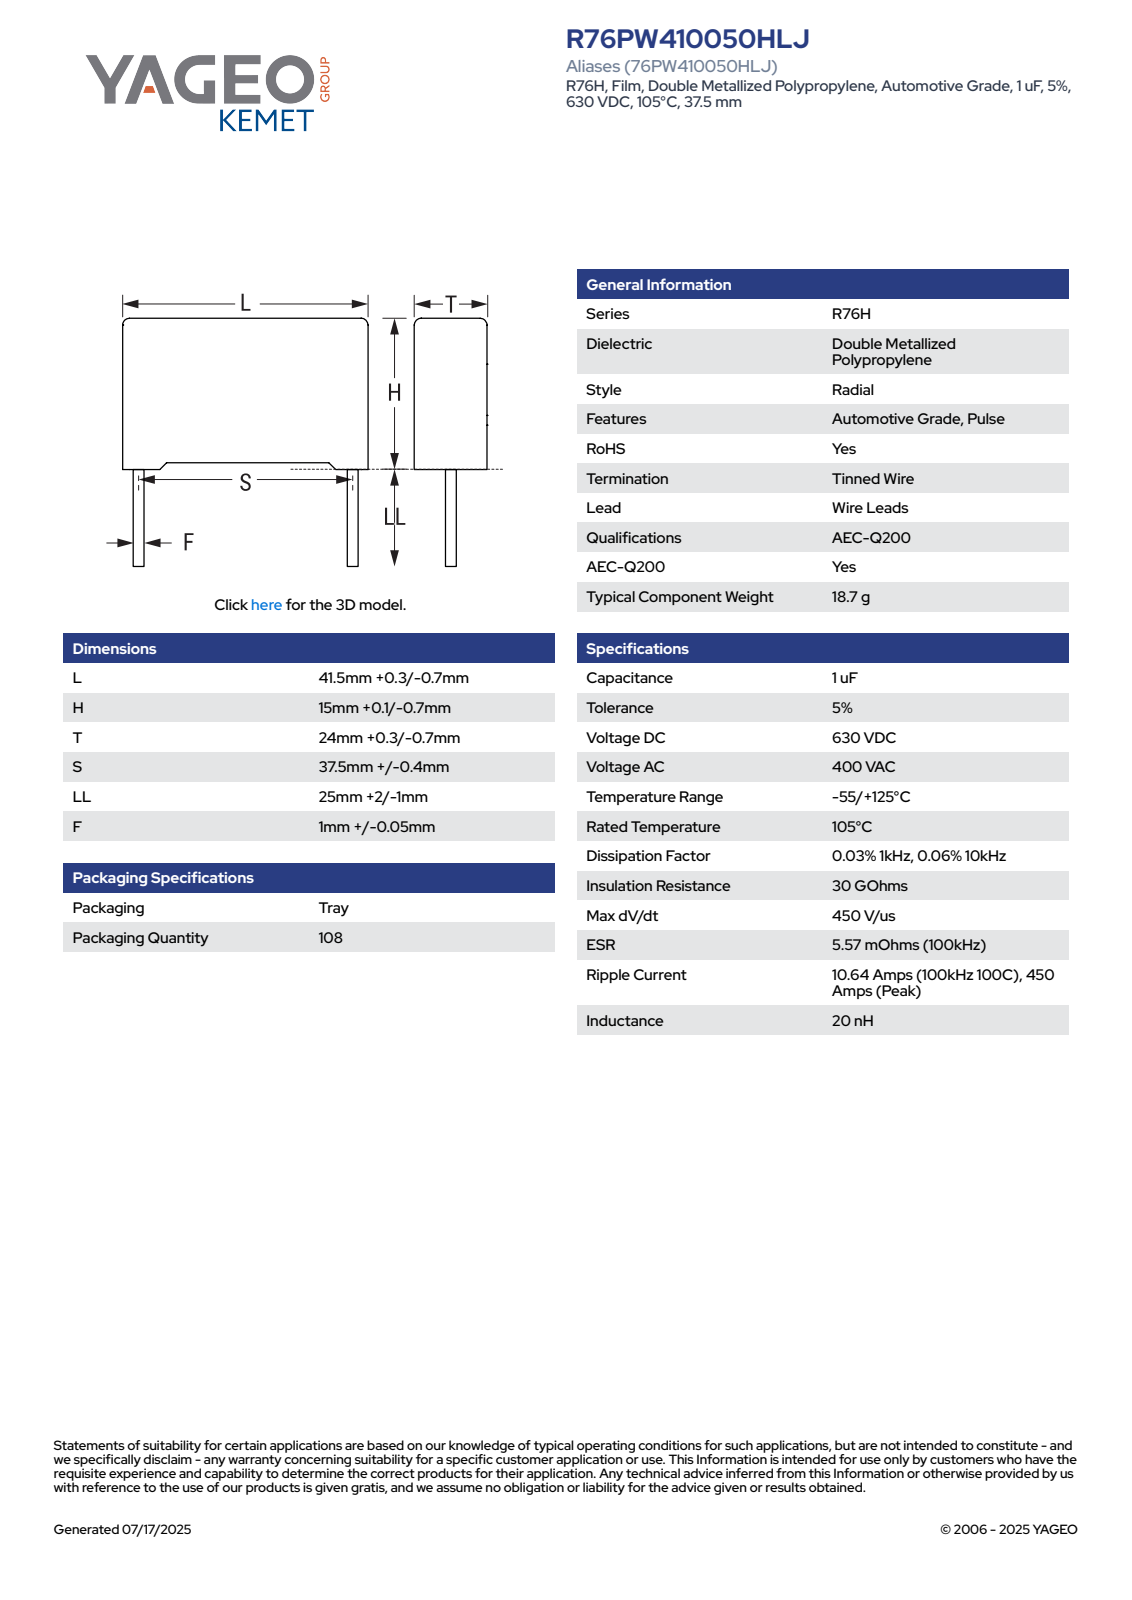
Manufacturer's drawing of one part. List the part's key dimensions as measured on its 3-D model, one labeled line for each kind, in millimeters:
Part name (STEP PRODUCT): CFR_RB2R76_41.5X15X24_L41.8H15.1T24.3S37.5LL27F1.05
STEP written by: SolidWorks 2014 (AUTOMOTIVE_DESIGN)
Units: millimetres
Bodies: 4 solids, 85 faces (77 planar, 8 cylindrical, 0 other)
Overall size (bounding box): 42.1 × 41.8 × 24.3
Volume: 14 701 mm³ · Surface area: 4 335 mm²
Round bosses / shafts (diameter × count): ⌀1.05 ×2
Partial cylindrical surfaces — rounded edges, fillets, slot ends (radius × count): R0.5 ×4
Main face-to-face distances: 14.35, 24.3, 41.8, 14.58, 0.52, 0.75, 15.1, 1.39, 40.41, 24.31
